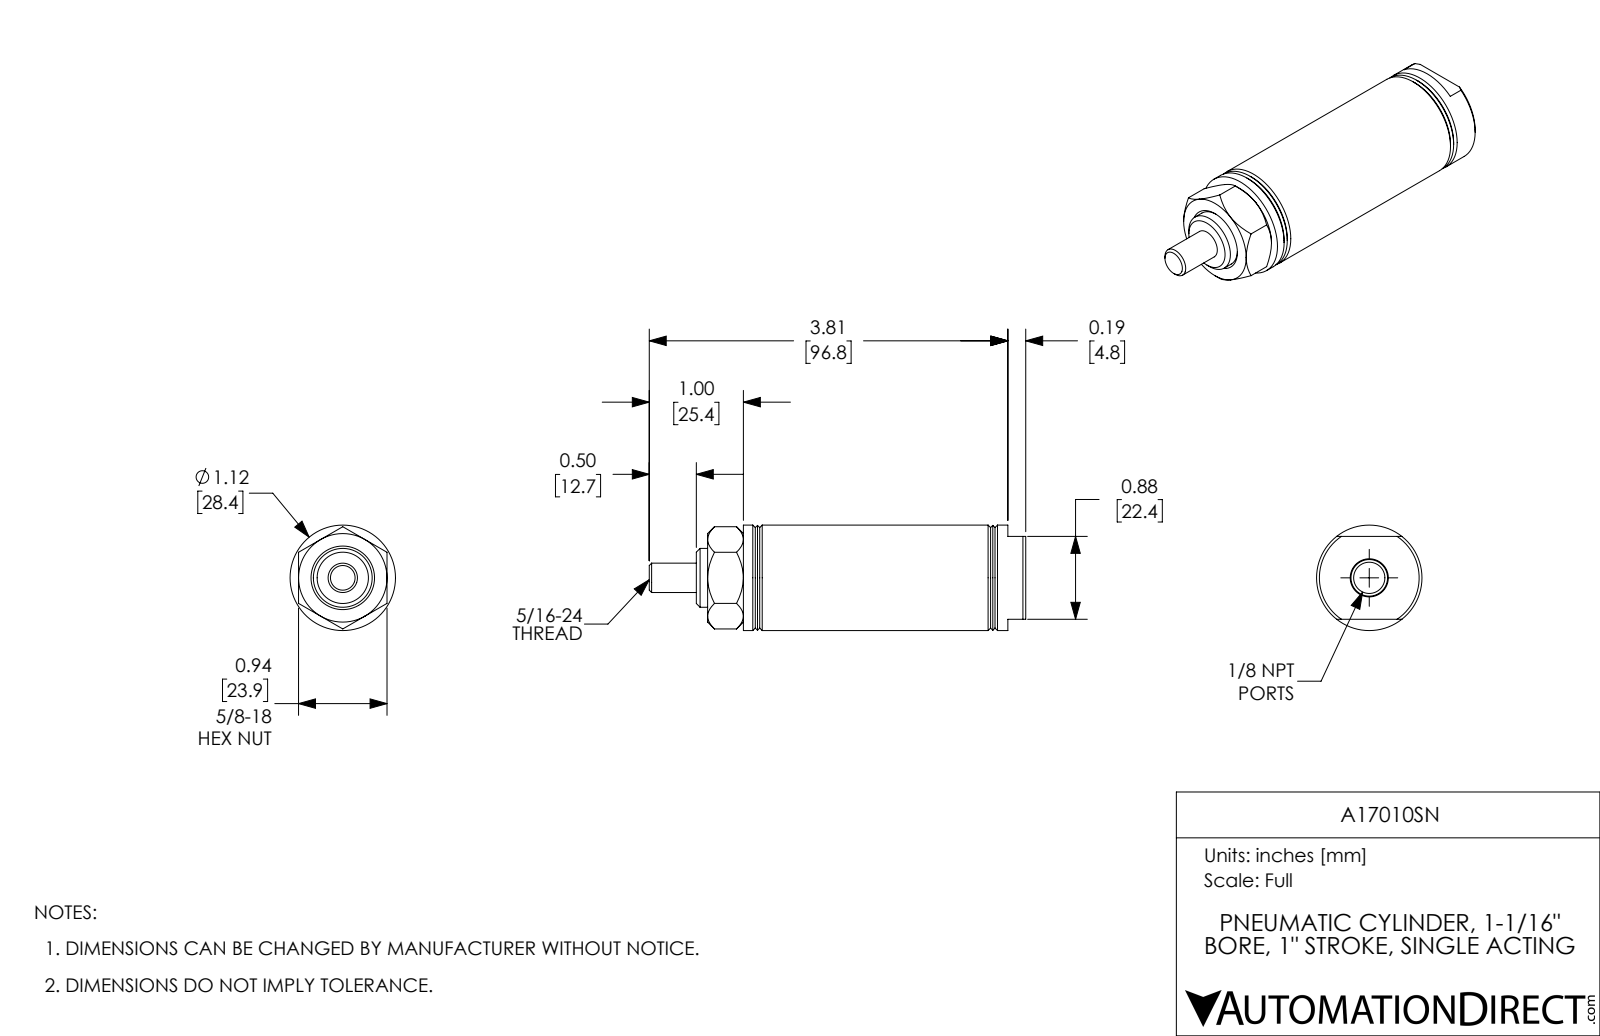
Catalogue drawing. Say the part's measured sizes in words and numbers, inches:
The part is named "A17010SN-Rod; A17010SN_Mounting Nut_D-9; A17010SN-MainBody; A17010SN". Its 3-D file was written by "SolidWorks 2017 (AUTOMOTIVE_DESIGN)". It is 3 solids with 82 faces: 21 planar, 20 cylindrical and 41 other. Overall it measures 4 by 1.12 by 1.12 inches. Its volume is 2.398 cubic inches and its surface area 31.04 square inches. Round holes: 1 of diameter 0.312, 1 of diameter 0.332, 1 of diameter 0.625, 1 of diameter 1.063. Round bosses or shafts: 1 of diameter 1.12. The main face-to-face distances are 2.25, 0.75, 0.5, 1, 1.75, 1.25, 1.5, 3, 0.94, 3.38.
